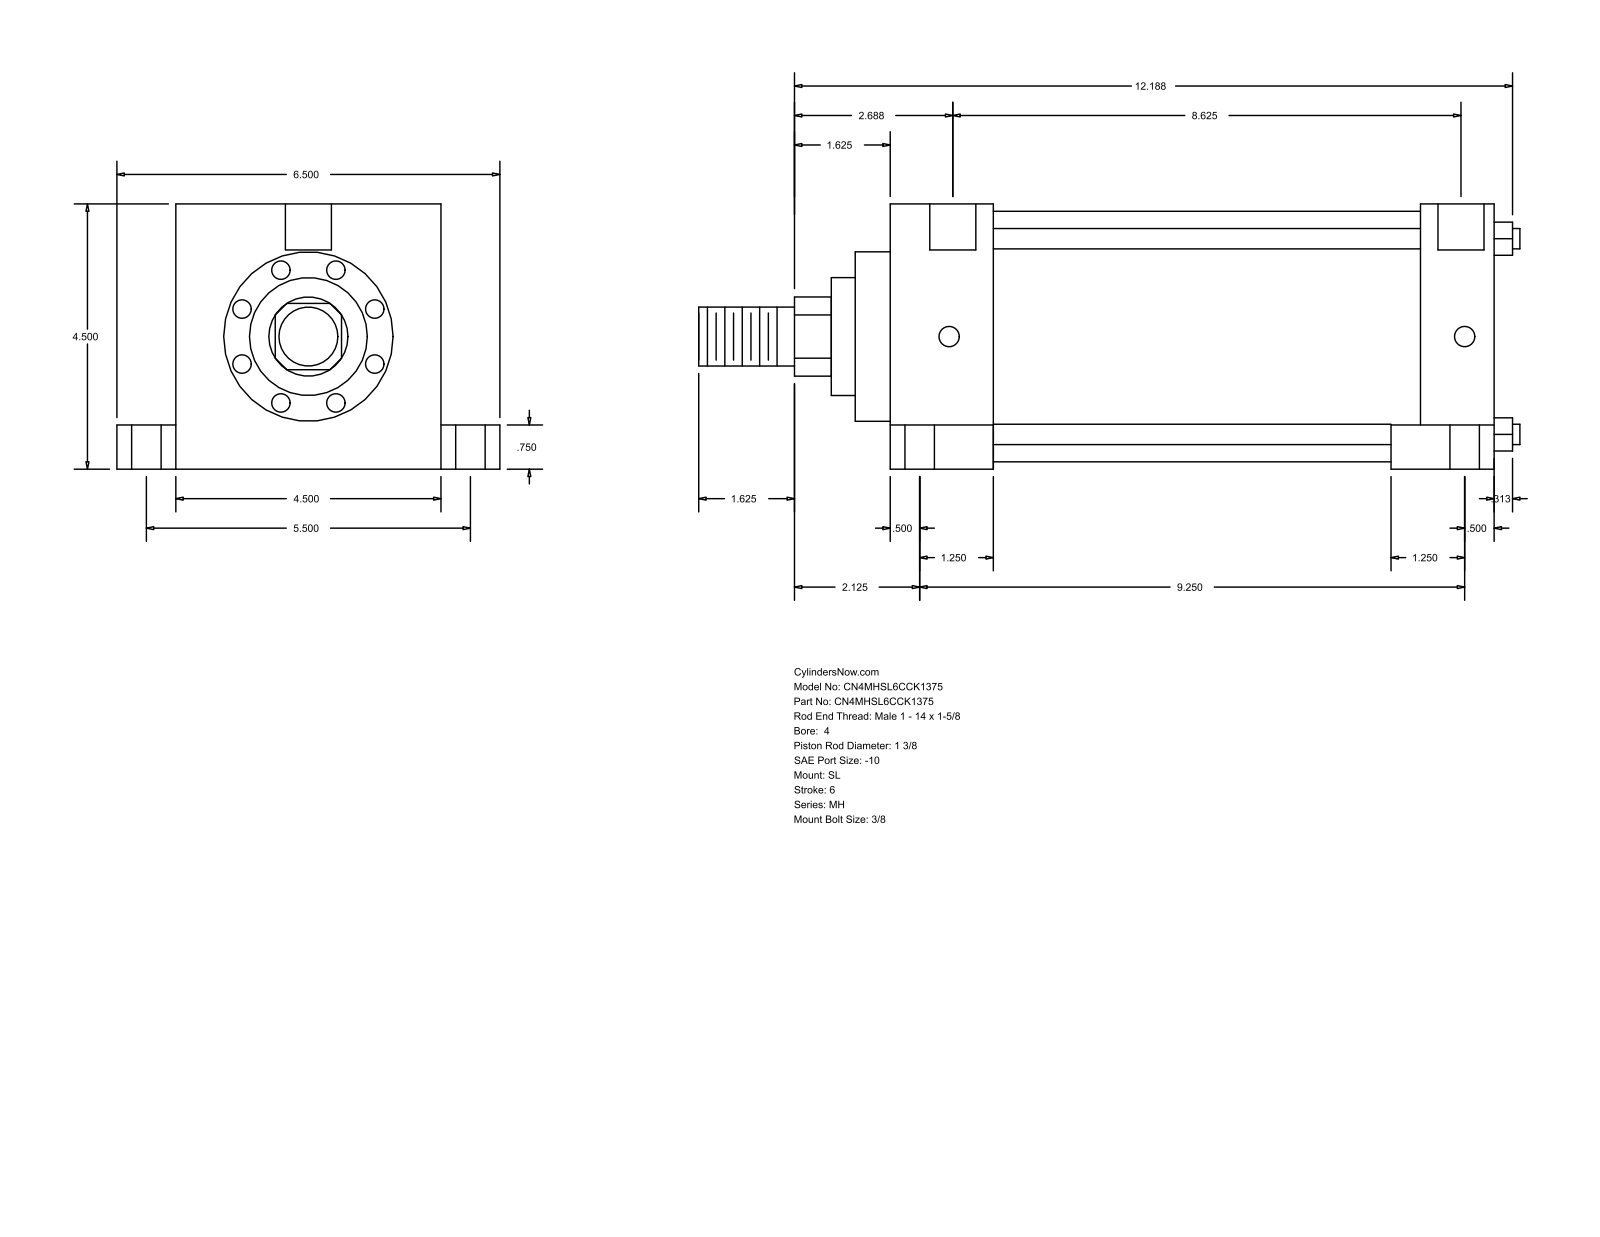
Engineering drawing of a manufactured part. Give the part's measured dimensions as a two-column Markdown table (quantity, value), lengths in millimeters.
| quantity | value |
| --- | --- |
| part name | MH_SL__0400_1.375 |
| STEP written by | GSSL Pune (CONFIG_CONTROL_DESIGN) |
| units | millimeters |
| bodies | 0 solids, 110 faces (77 planar, 33 cylindrical, 0 other) |
| overall size | 354.01 × 165.1 × 114.3 |
| round holes (diameter × count) | 8.73 × 4, 12.7 × 4, 19.05 × 4, 19.84 × 2 |
| round bosses / shafts (diameter × count) | 8.76 × 4, 107.95 × 1, 73.03 × 1, 50.8 × 1, 34.92 × 1, 25.4 × 1 |
| partial cylindrical surfaces (radius × count) | 17.06 × 1 |
| main face-to-face distances | 114.3, 260.35, 44.45, 215.9, 228.61, 184.16, 31.74, 25.4, 139.7, 19.05 |
| hole center spacings | 1.59, 69.85, 69.87, 70.99, 71.29, 139.7, 220.67, 222.26 |
